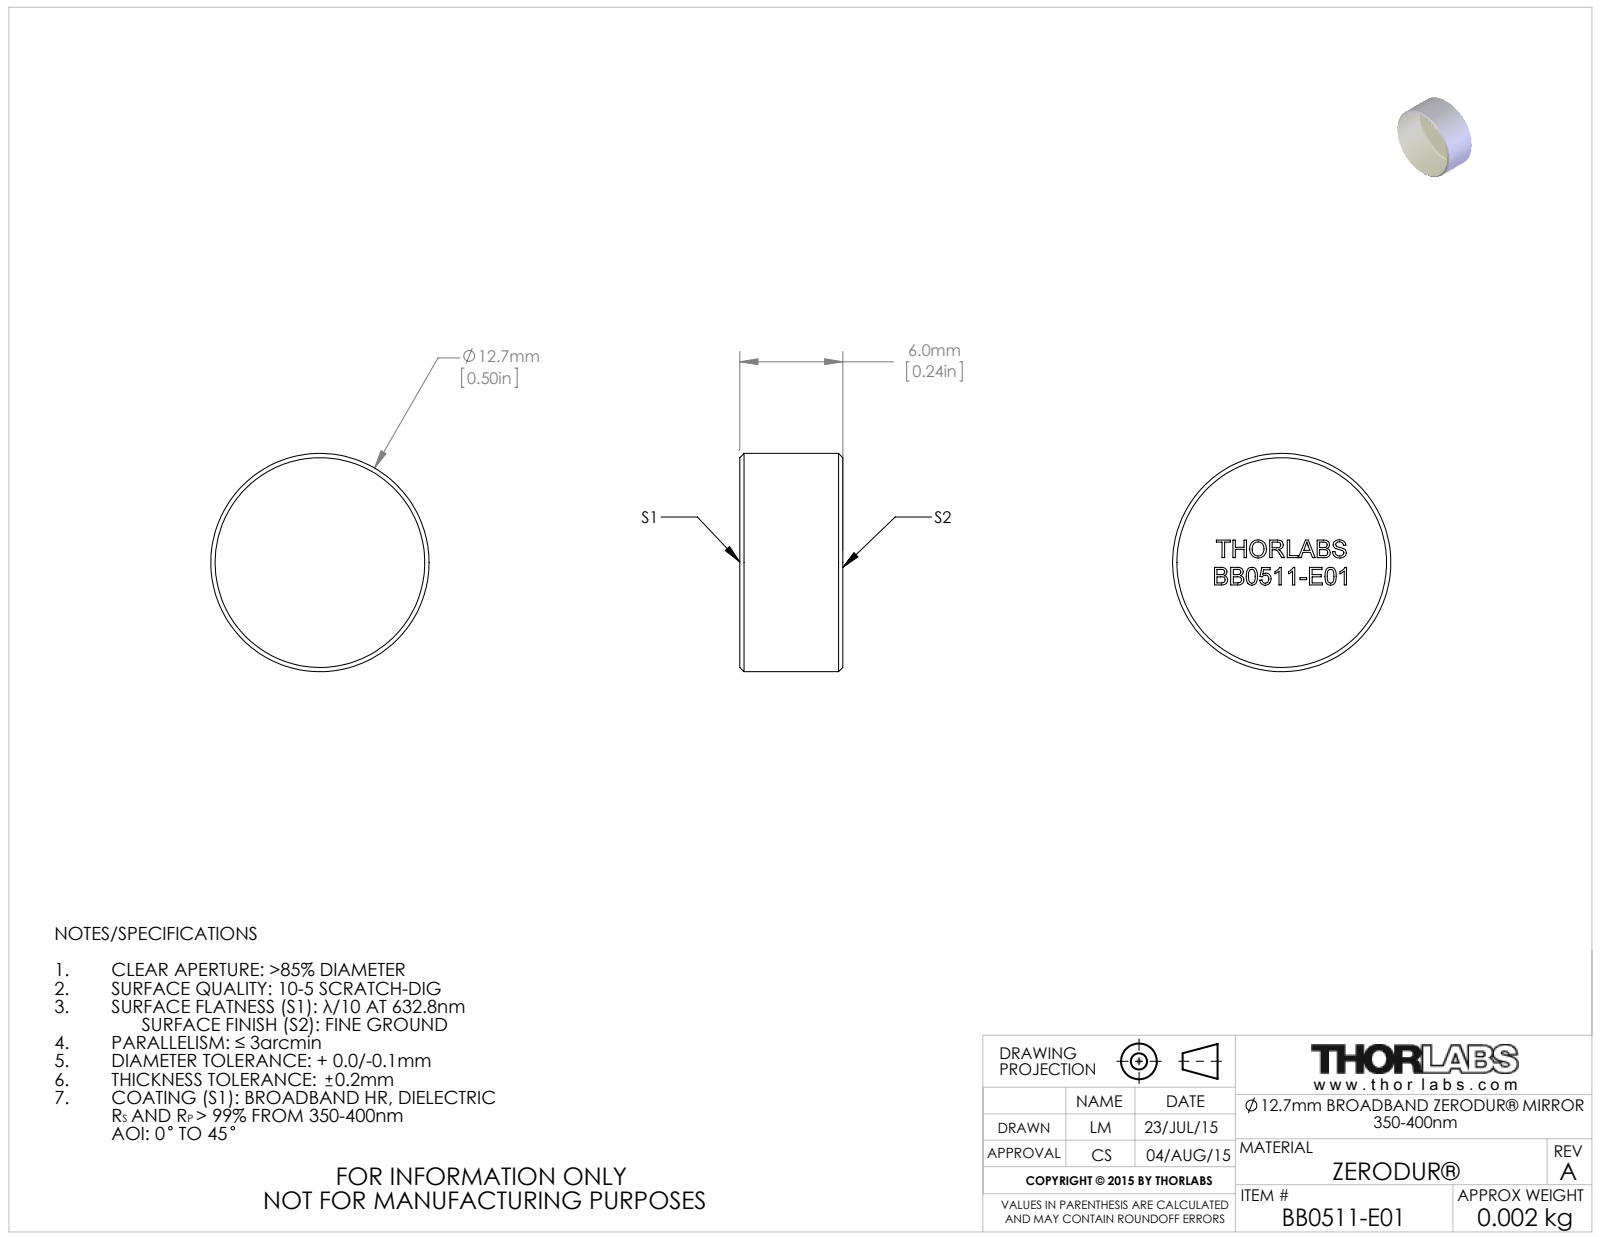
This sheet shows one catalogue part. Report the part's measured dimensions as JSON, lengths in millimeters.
{"part_name": "TTN045132-E0W", "step_written_by": "SolidWorks 2014 (CONFIG_CONTROL_DESIGN)", "units": "millimeters", "bodies": {"solids": 1, "faces": 249, "planar": 146, "cylindrical": 2, "other": 101}, "overall_size": [12.7, 12.7, 6], "volume_mm3": 758, "surface_area_mm2": 481, "round_bosses_or_shafts": [[12.7, 1]], "face_to_face_distances": [6, 1.58, 0.79, 0.44, 0.91, 1.03, 2.02, 1.46, 1.28, 3.01]}
